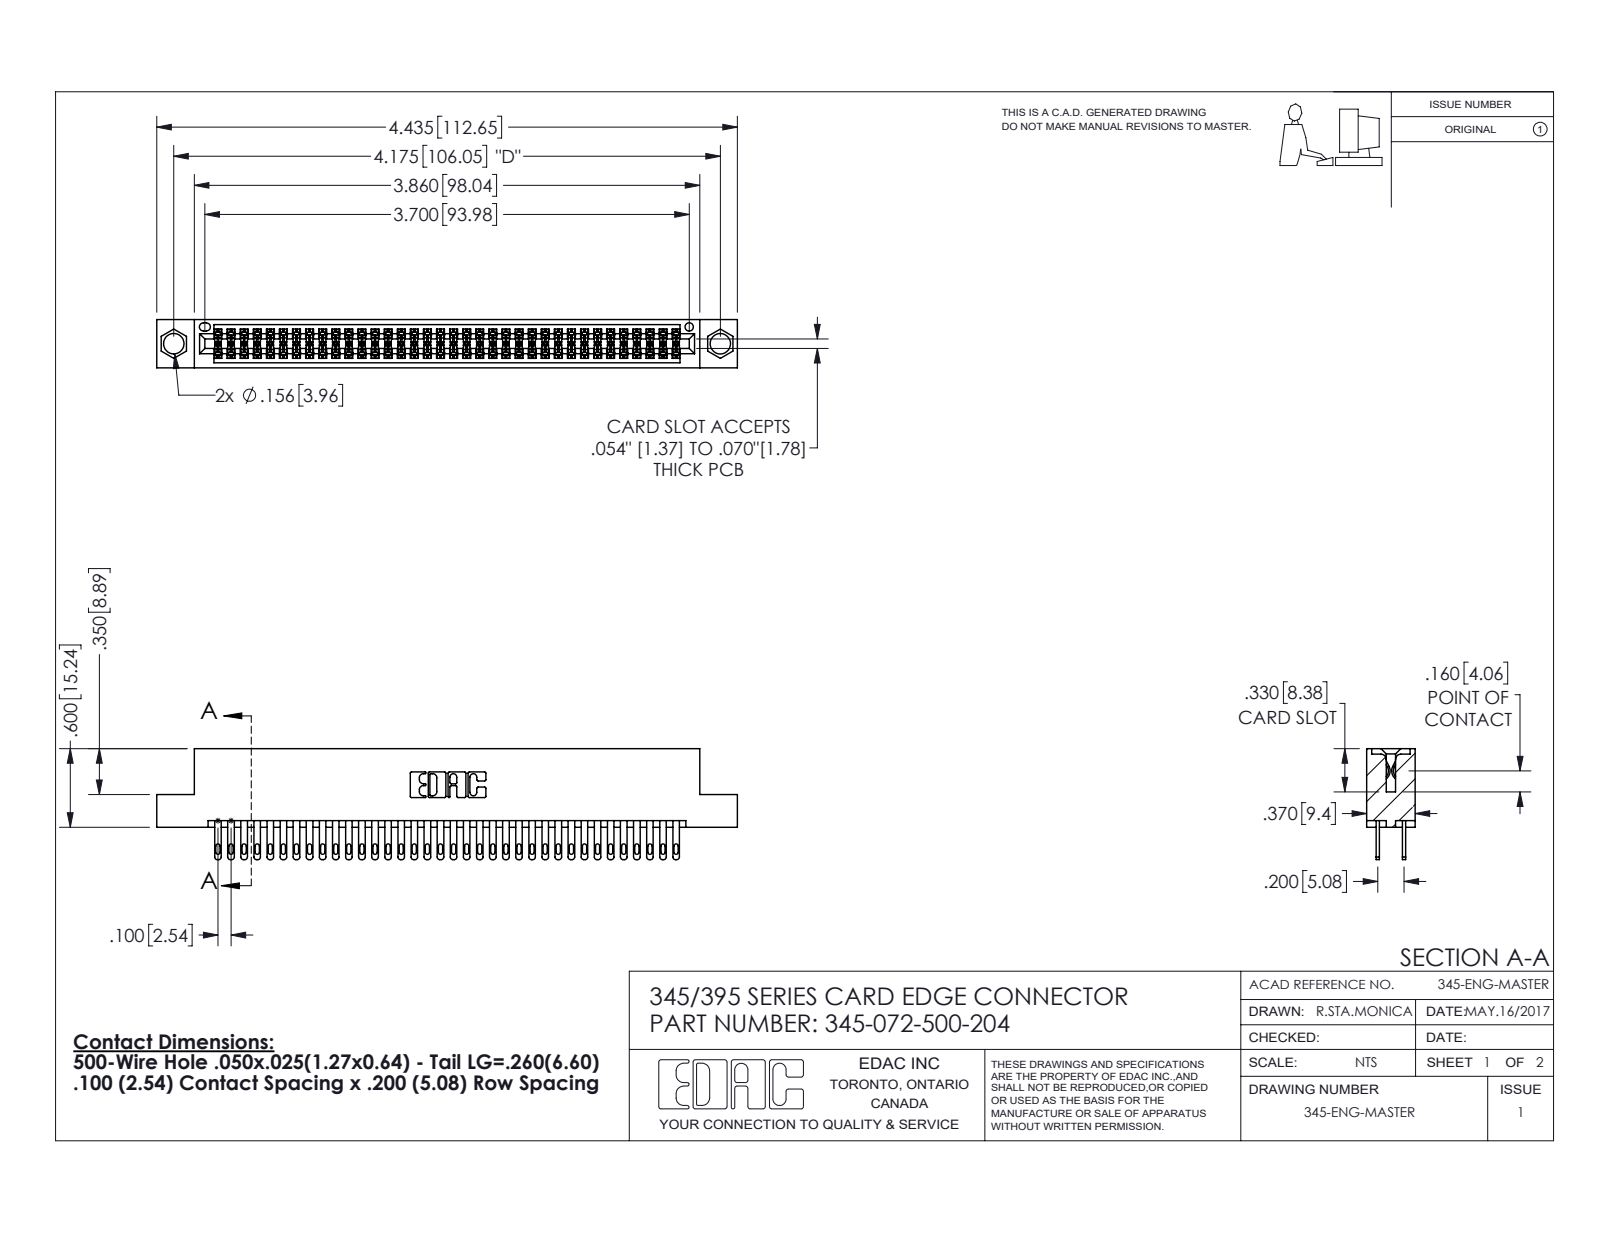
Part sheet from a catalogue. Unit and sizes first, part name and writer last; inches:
Units: inches
Overall size (bounding box): 4.435 × 0.847 × 0.37
Round holes (diameter × count): ⌀0.156 ×2, ⌀0.064 ×1
Partial cylindrical surfaces — rounded edges, fillets, slot ends (radius × count): R0.006 ×108, R0.016 ×72, R0.02 ×72, R0.01 ×22, R0.007 ×6, R0.031 ×6, R0.026 ×3, R0.014 ×2
Main face-to-face distances: 0.298, 0.072, 0.2, 0.098, 0.272, 0.025, 0.37, 0.225, 0.175, 0.149
Hole centre spacings: 0.27, 3.939, 4.175
Volume: 0.671 in³ · Surface area: 25.93 in²
Bodies: 73 solids, 3452 faces (2038 planar, 1414 cylindrical, 0 other)
Part name (STEP PRODUCT): 345-072-500-204; 345-292-001_345-293-100; 345 Part_Flush Mounting Lugs - 0.156 Dia-TI
STEP written by: SolidWorks 2020 (CONFIG_CONTROL_DESIGN)
